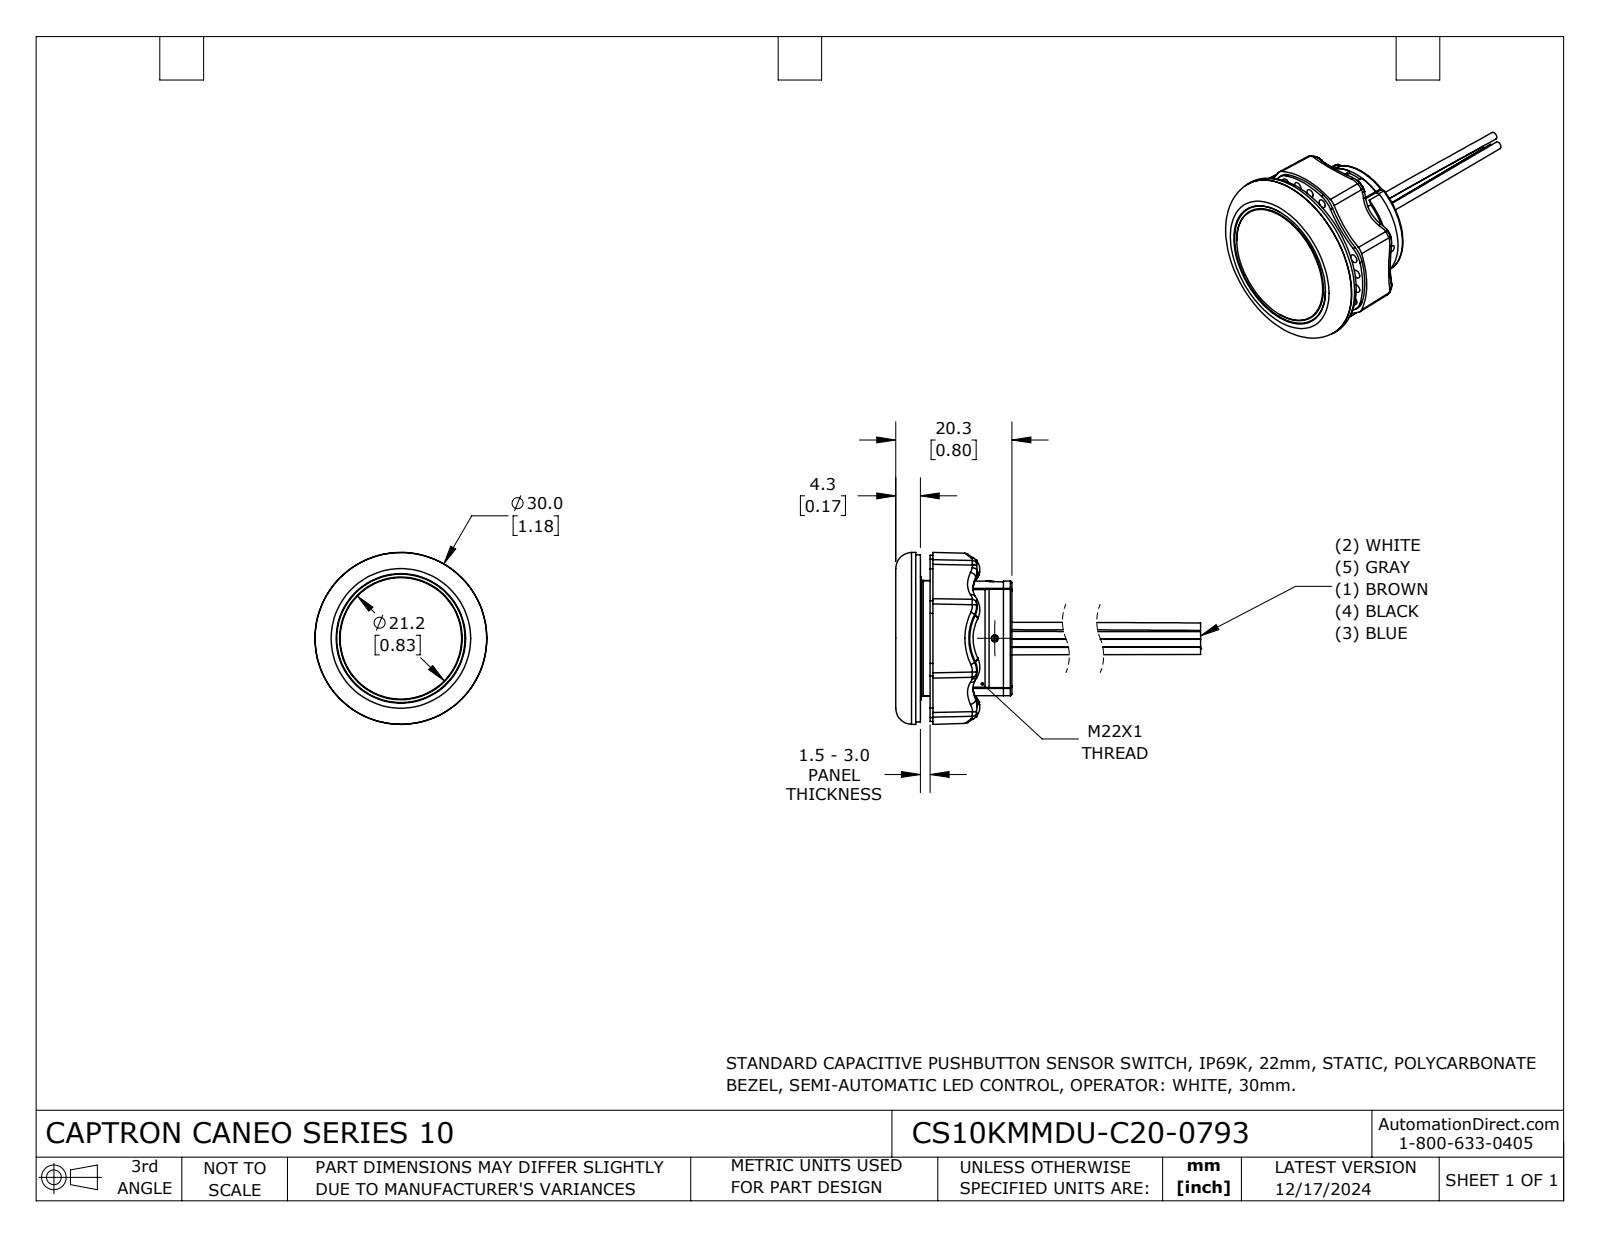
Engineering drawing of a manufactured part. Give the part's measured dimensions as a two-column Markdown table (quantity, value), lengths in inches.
| quantity | value |
| --- | --- |
| part name | CS10KMMDU-C20-0793 |
| STEP written by | SolidWorks 2024 (CONFIG_CONTROL_DESIGN) |
| units | inches |
| bodies | 7 solids, 601 faces (204 planar, 75 cylindrical, 322 other) |
| overall size | 2.049 × 1.181 × 1.181 |
| volume | 0.649 in³ |
| surface area | 9.995 in² |
| round holes (diameter × count) | 0.047 × 1, 0.827 × 1, 0.927 × 1 |
| round bosses / shafts (diameter × count) | 1.181 × 1, 1.15 × 1, 0.72 × 1, 0.717 × 1 |
| partial cylindrical surfaces (radius × count) | 0.012 × 8, 0.004 × 6, 0.01 × 6, 0.295 × 6, 0.02 × 4, 0.039 × 4, 0.689 × 4, 0.362 × 1 |
| main face-to-face distances | 0.169, 0.63, 0.799, 0.067, 0.563, 0.236, 0.079, 0.551, 0.248, 0.242 |
